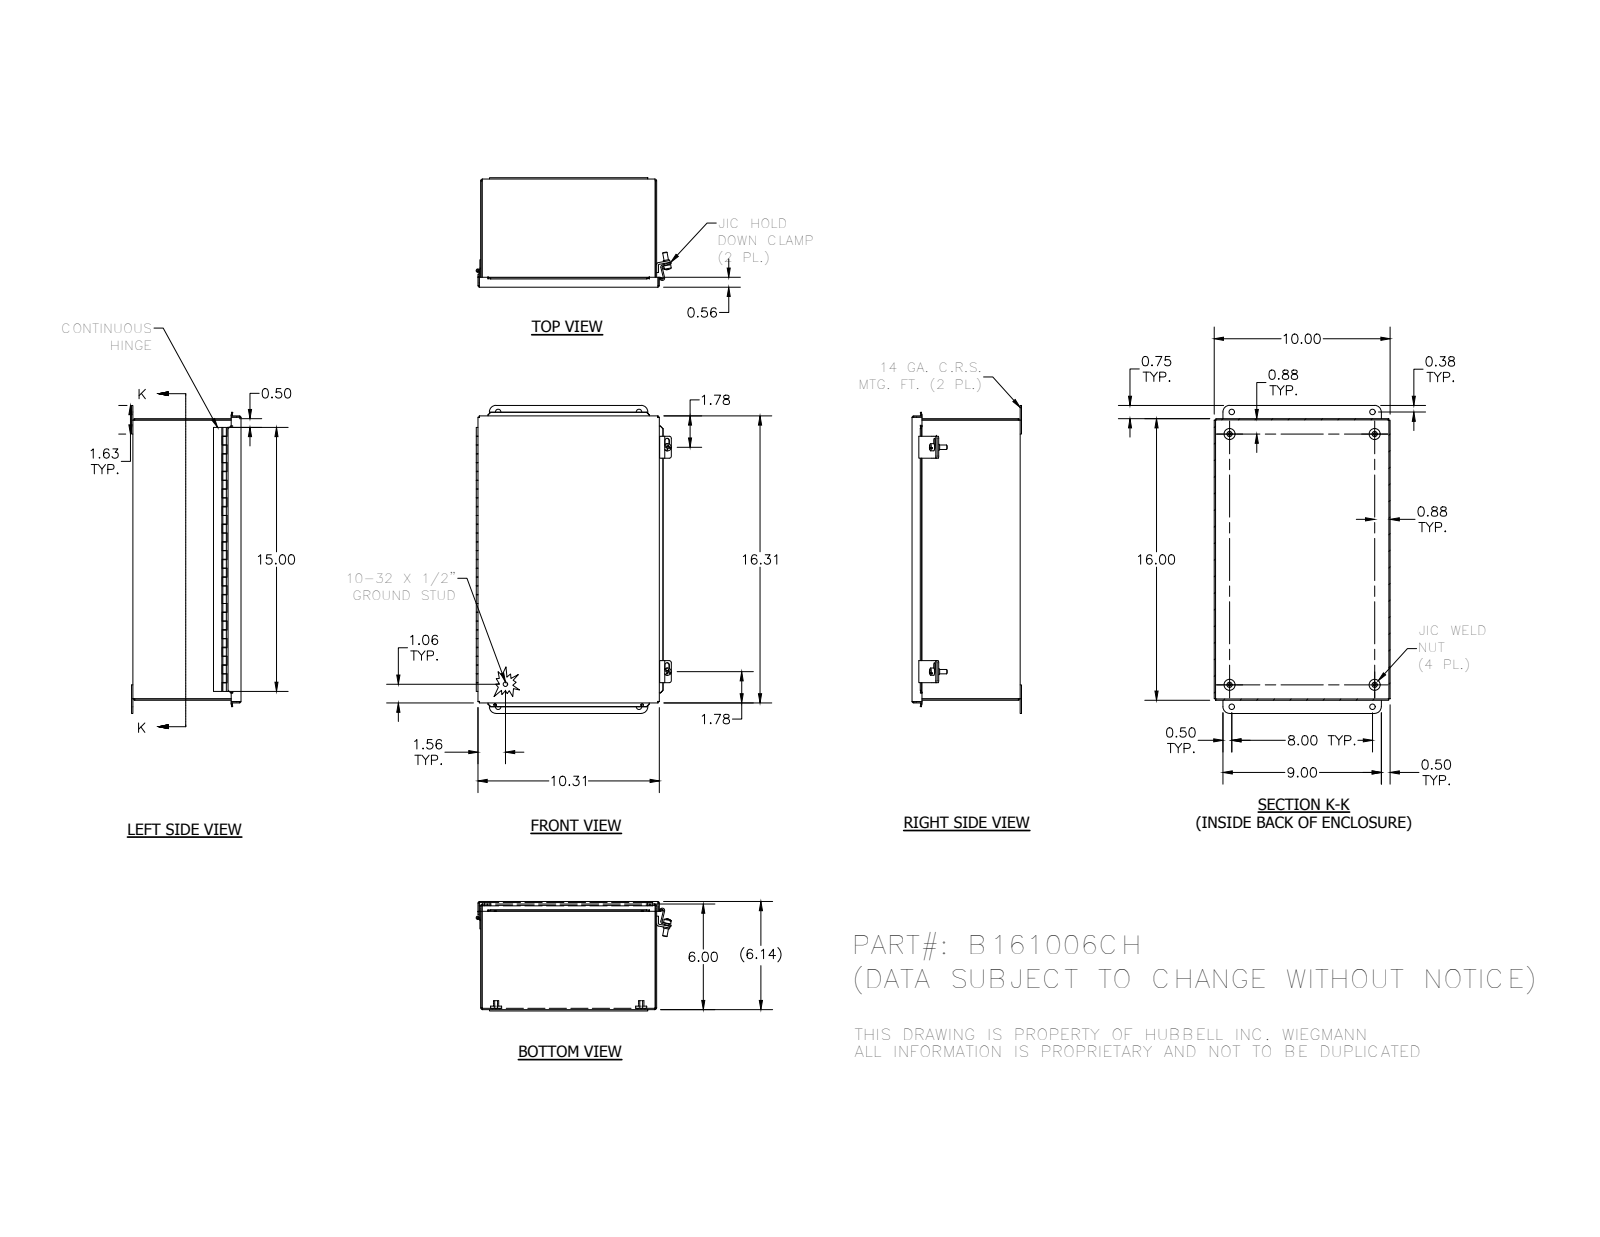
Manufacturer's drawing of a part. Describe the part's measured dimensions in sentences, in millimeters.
The part is named "B161006CH; 3499; 3484; C1001 (+8 more)". Its 3-D file was written by "Autodesk Inventor 2012 (AUTOMOTIVE_DESIGN)". It is 20 solids with 539 faces: 347 planar, 147 cylindrical and 45 other. Overall it measures 444.5 by 281.6 by 158 millimeters. Its volume is 950 600 cubic millimeters and its surface area 1 030 000 square millimeters. Round holes: 4 of diameter 4, 4 of diameter 7.9, 2 of diameter 3.6, 2 of diameter 5, 1 of diameter 2.9. Round bosses or shafts: 4 of diameter 15.9, 4 of diameter 7.6, 3 of diameter 6.4, 2 of diameter 10.4, 2 of diameter 8.7, 1 of diameter 5.1, 1 of diameter 4.8, 1 of diameter 2.5. Partial cylindrical surfaces (rounded edges, fillets, slot ends): 15 of radius 0.8, 8 of radius 2.7, 8 of radius 3.2, 7 of radius 2.4, 4 of radius 3.4, 4 of radius 9.5, 3 of radius 1.6, 3 of radius 3.2. The main face-to-face distances are 1.9, 154.5, 252.1, 1.6, 156.1, 152.6, 154.2, 404.5, 254, 250.2. The hole center spacings are 393.7, 31.9, 203.2, 208.8, 208.8, 209.6, 418.2, 444.5.
